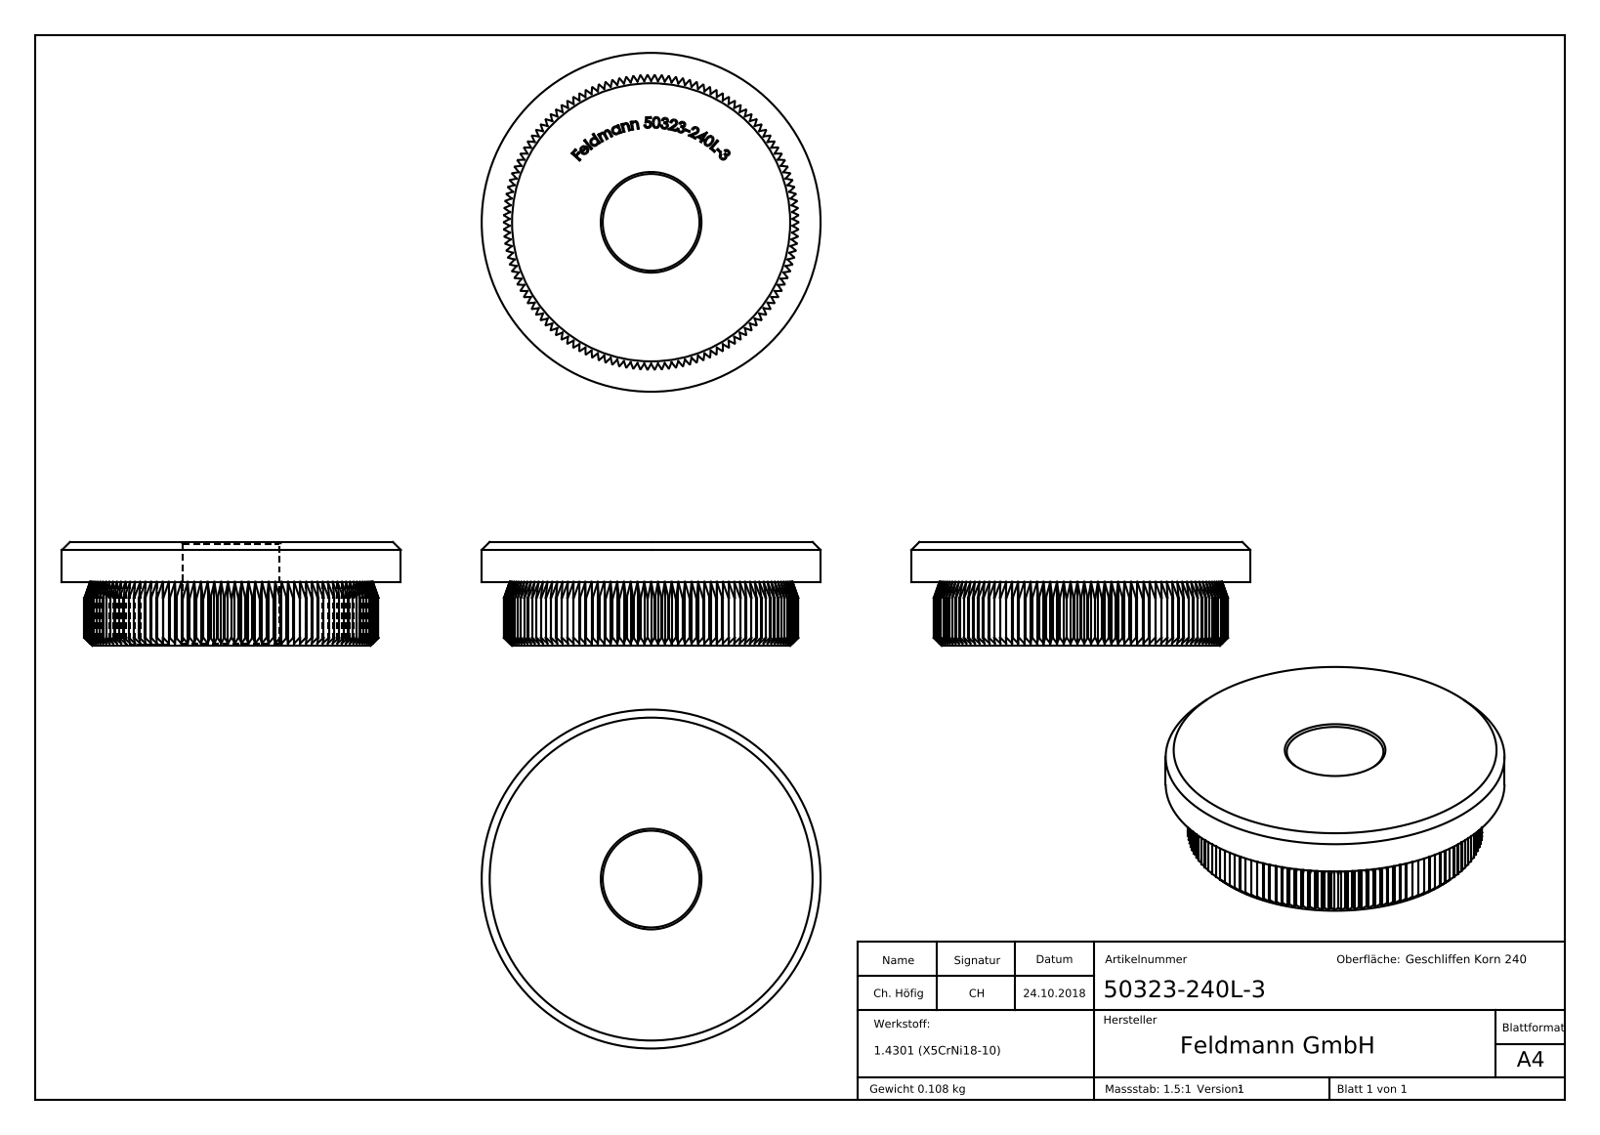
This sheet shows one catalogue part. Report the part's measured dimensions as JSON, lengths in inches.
{"part_name": "50323-240L-3", "step_written_by": "SolidWorks 2015 (CONFIG_CONTROL_DESIGN)", "units": "inches", "bodies": {"solids": 1, "faces": 799, "planar": 413, "cylindrical": 134, "other": 252}, "overall_size": [1.669, 1.669, 0.512], "volume_in3": 0.833, "surface_area_in2": 8.156, "round_holes": [[0.476, 1]], "round_bosses_or_shafts": [[1.669, 1]], "partial_cylinders_radius": [[0.724, 1]], "face_to_face_distances": [0.512, 0.697, 0.315, 0.197, 0.698, 0.696, 0.311, 0.508, 0.021, 0.046]}
